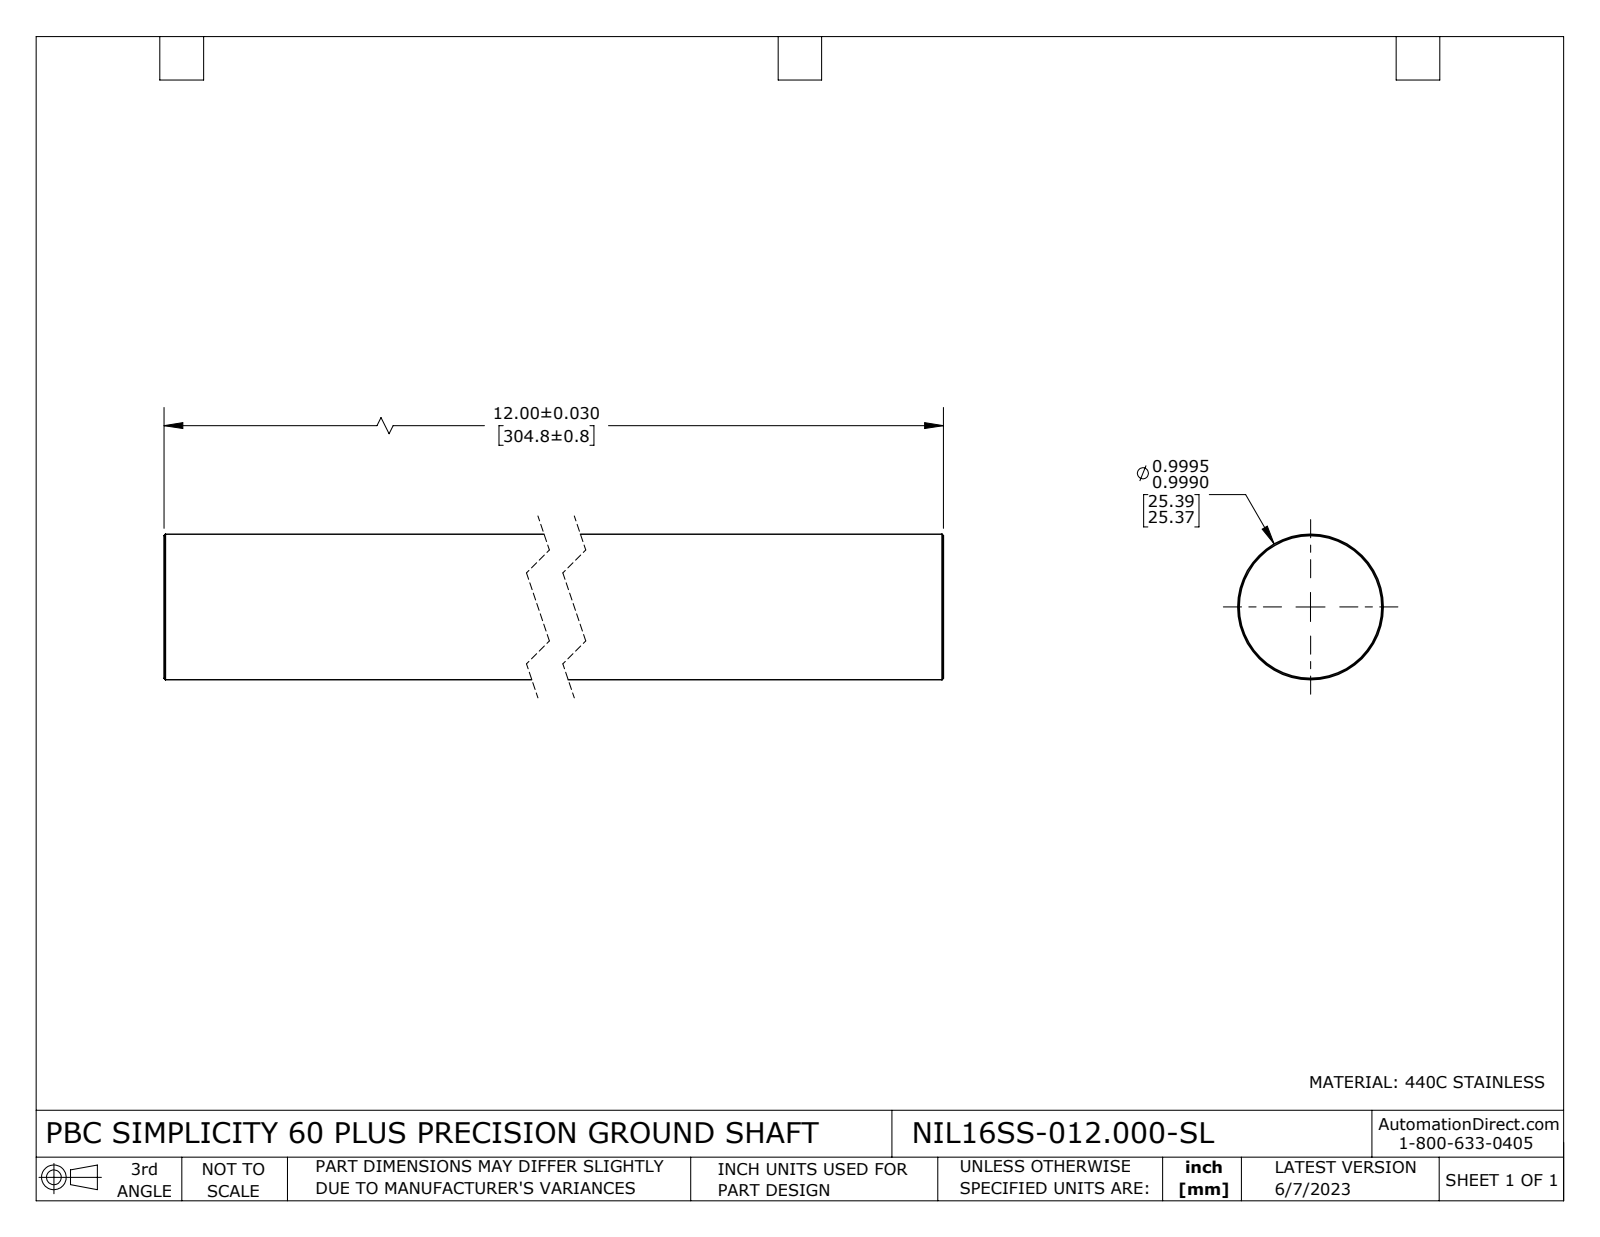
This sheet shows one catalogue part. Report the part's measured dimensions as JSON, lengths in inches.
{"part_name": "NIL16SS-012.000-SL", "step_written_by": "SolidWorks 2021 (CONFIG_CONTROL_DESIGN)", "units": "inches", "bodies": {"solids": 1, "faces": 8, "planar": 2, "cylindrical": 2, "other": 4}, "overall_size": [12, 1, 1], "volume_in3": 9.424, "surface_area_in2": 39.23, "round_bosses_or_shafts": [[1, 1]], "face_to_face_distances": [12]}
